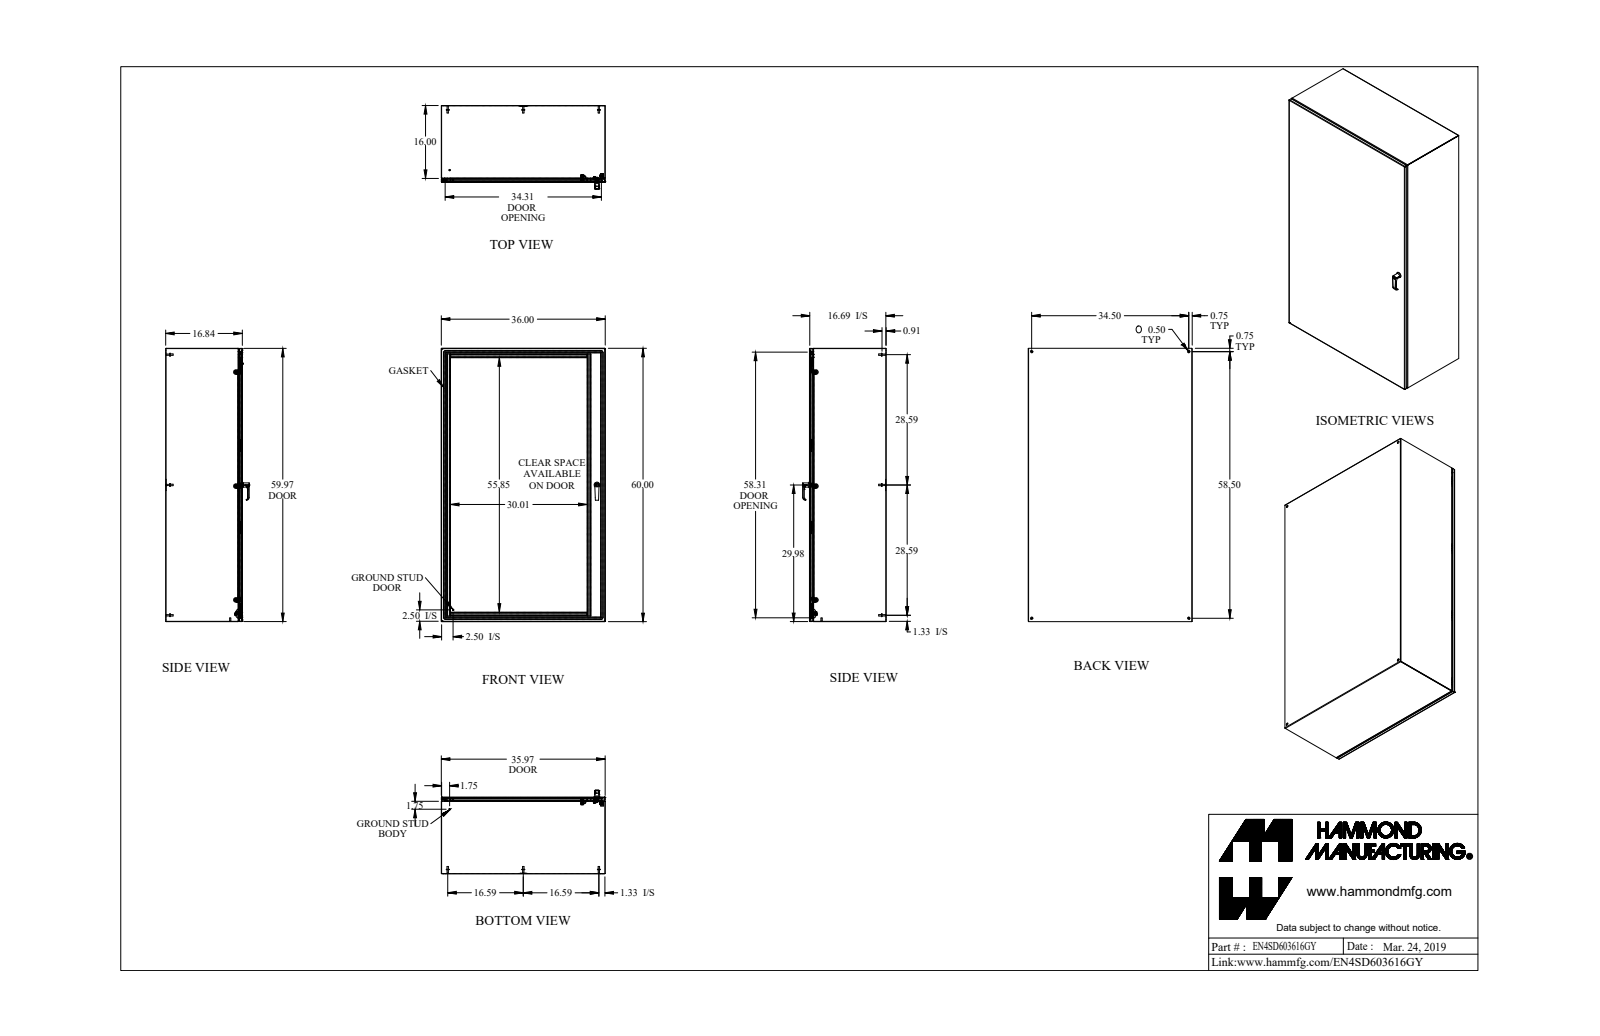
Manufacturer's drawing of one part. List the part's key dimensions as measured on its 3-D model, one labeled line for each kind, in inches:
Part name (STEP PRODUCT): EN4SD603616GY
STEP written by: SolidWorks 2018 (AUTOMOTIVE_DESIGN)
Units: inches
Bodies: 63 solids, 1713 faces (757 planar, 634 cylindrical, 322 other)
Overall size (bounding box): 60 × 36 × 18.367
Volume: 607.4 in³ · Surface area: 17 112 in²
Round holes (diameter × count): ⌀0.176 ×6, ⌀0.196 ×4, ⌀0.5 ×4, ⌀0.25 ×3, ⌀0.265 ×3, ⌀0.413 ×3, ⌀0.256 ×2, ⌀0.313 ×2, ⌀0.394 ×2, ⌀0.172 ×1, ⌀0.24 ×1, ⌀0.242 ×1
Round bosses / shafts (diameter × count): ⌀0.313 ×8, ⌀0.27 ×8, ⌀0.25 ×7, ⌀0.625 ×6, ⌀0.156 ×6, ⌀0.375 ×4, ⌀1 ×3, ⌀0.625 ×3
Partial cylindrical surfaces — rounded edges, fillets, slot ends (radius × count): R0.043 ×24, R0.036 ×18, R0.108 ×18, R0.062 ×17, R0.03 ×15, R0.094 ×10, R0.016 ×9, R0.006 ×8
Main face-to-face distances: 0.072, 16.765, 16.693, 16.837, 35.928, 59.928, 35.856, 36, 59.856, 60
Hole centre spacings: 4.398, 24.981, 25, 25.019, 33.698, 34.5, 50, 54.245
